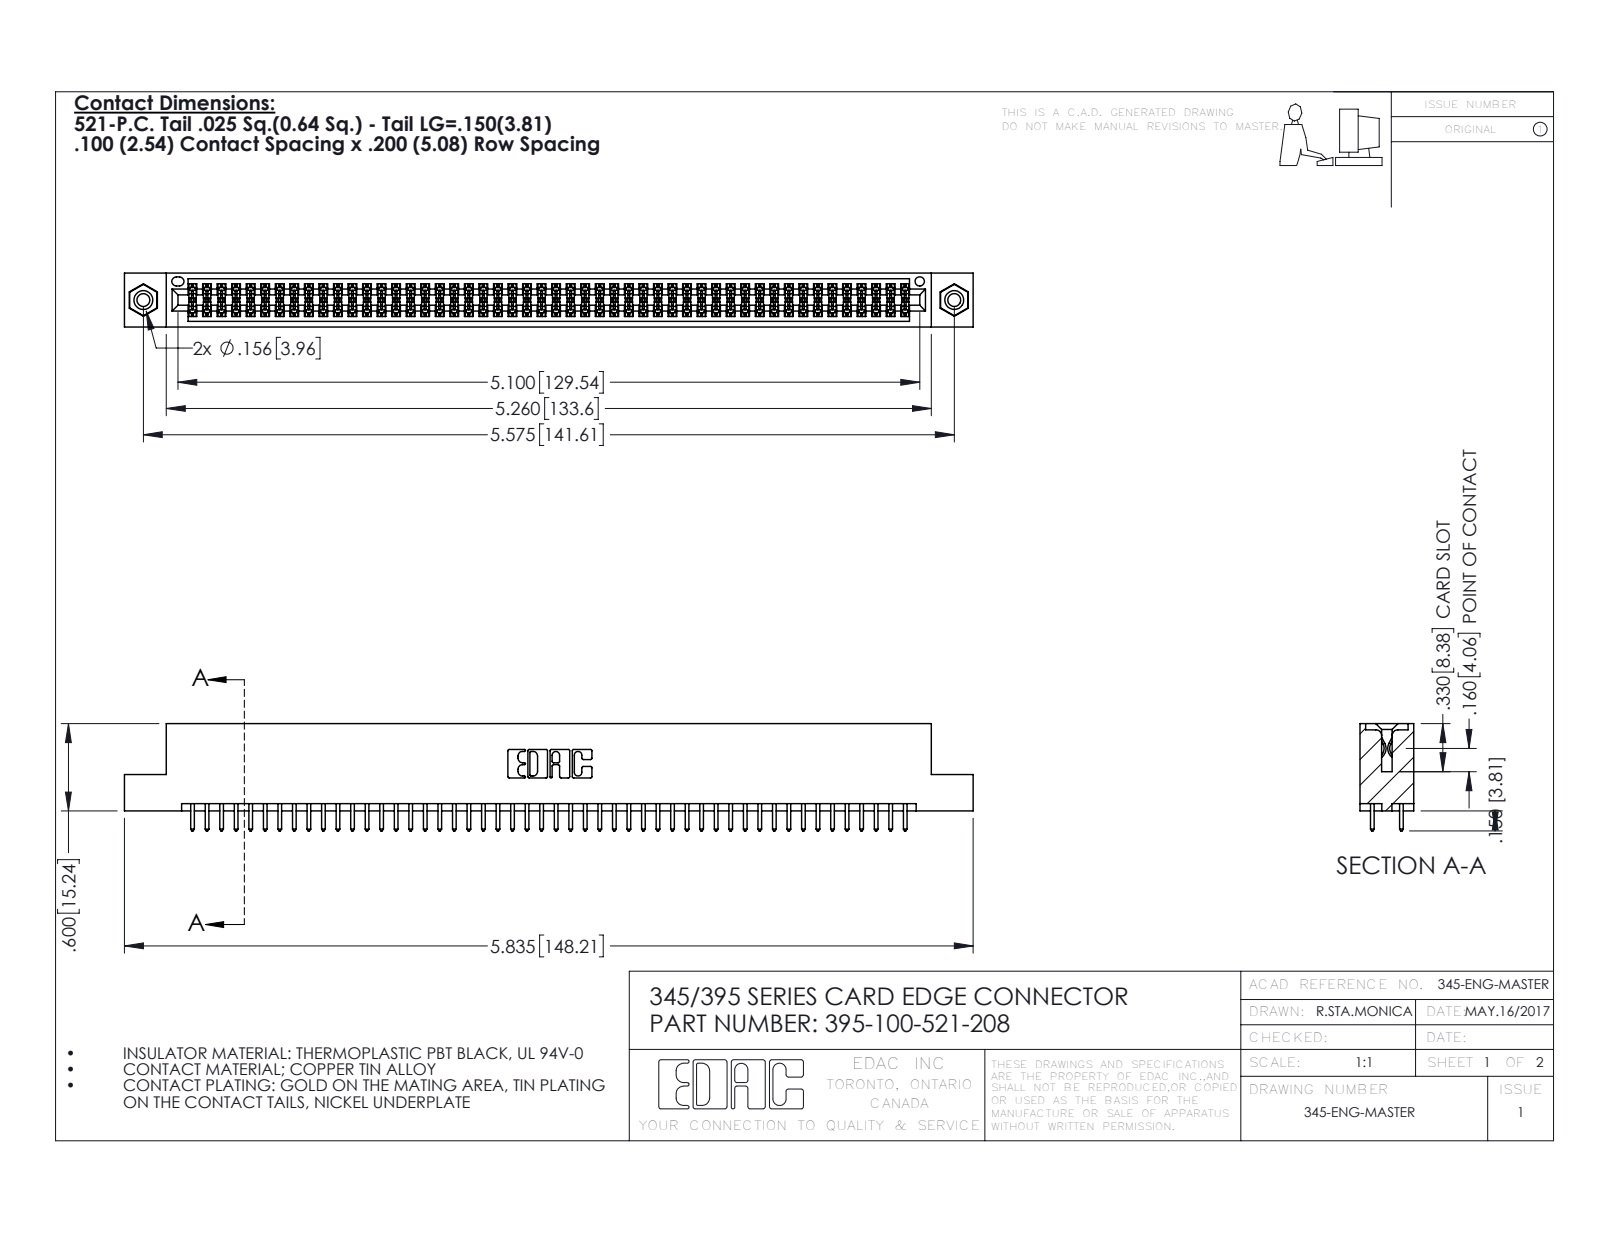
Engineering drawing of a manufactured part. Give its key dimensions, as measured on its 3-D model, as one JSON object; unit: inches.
{"part_name": "345 Part_Flush Mounting Lugs - 0.156 Dia-TI; 345-292-001_345-293-121; 345-250-001_345-250-003-102; 395-100-521-208", "step_written_by": "SolidWorks 2016 (CONFIG_CONTROL_DESIGN)", "units": "inches", "bodies": {"solids": 103, "faces": 5186, "planar": 3412, "cylindrical": 1758, "other": 16}, "overall_size": [5.835, 0.737, 0.37], "volume_in3": 0.88, "surface_area_in2": 32.9, "round_holes": [[0.089, 2], [0.125, 2], [0.156, 2], [0.064, 1]], "round_bosses_or_shafts": [[0.155, 2]], "partial_cylinders_radius": [[0.006, 150], [0.01, 100], [0.01, 22], [0.007, 6], [0.031, 6], [0.026, 3], [0.014, 2], [0.019, 2]], "face_to_face_distances": [0.072, 0.298, 0.2, 0.37, 0.098, 0.272, 0.025, 0.225, 0.175, 0.149], "hole_center_spacings": [0.27, 5.339, 5.575]}
